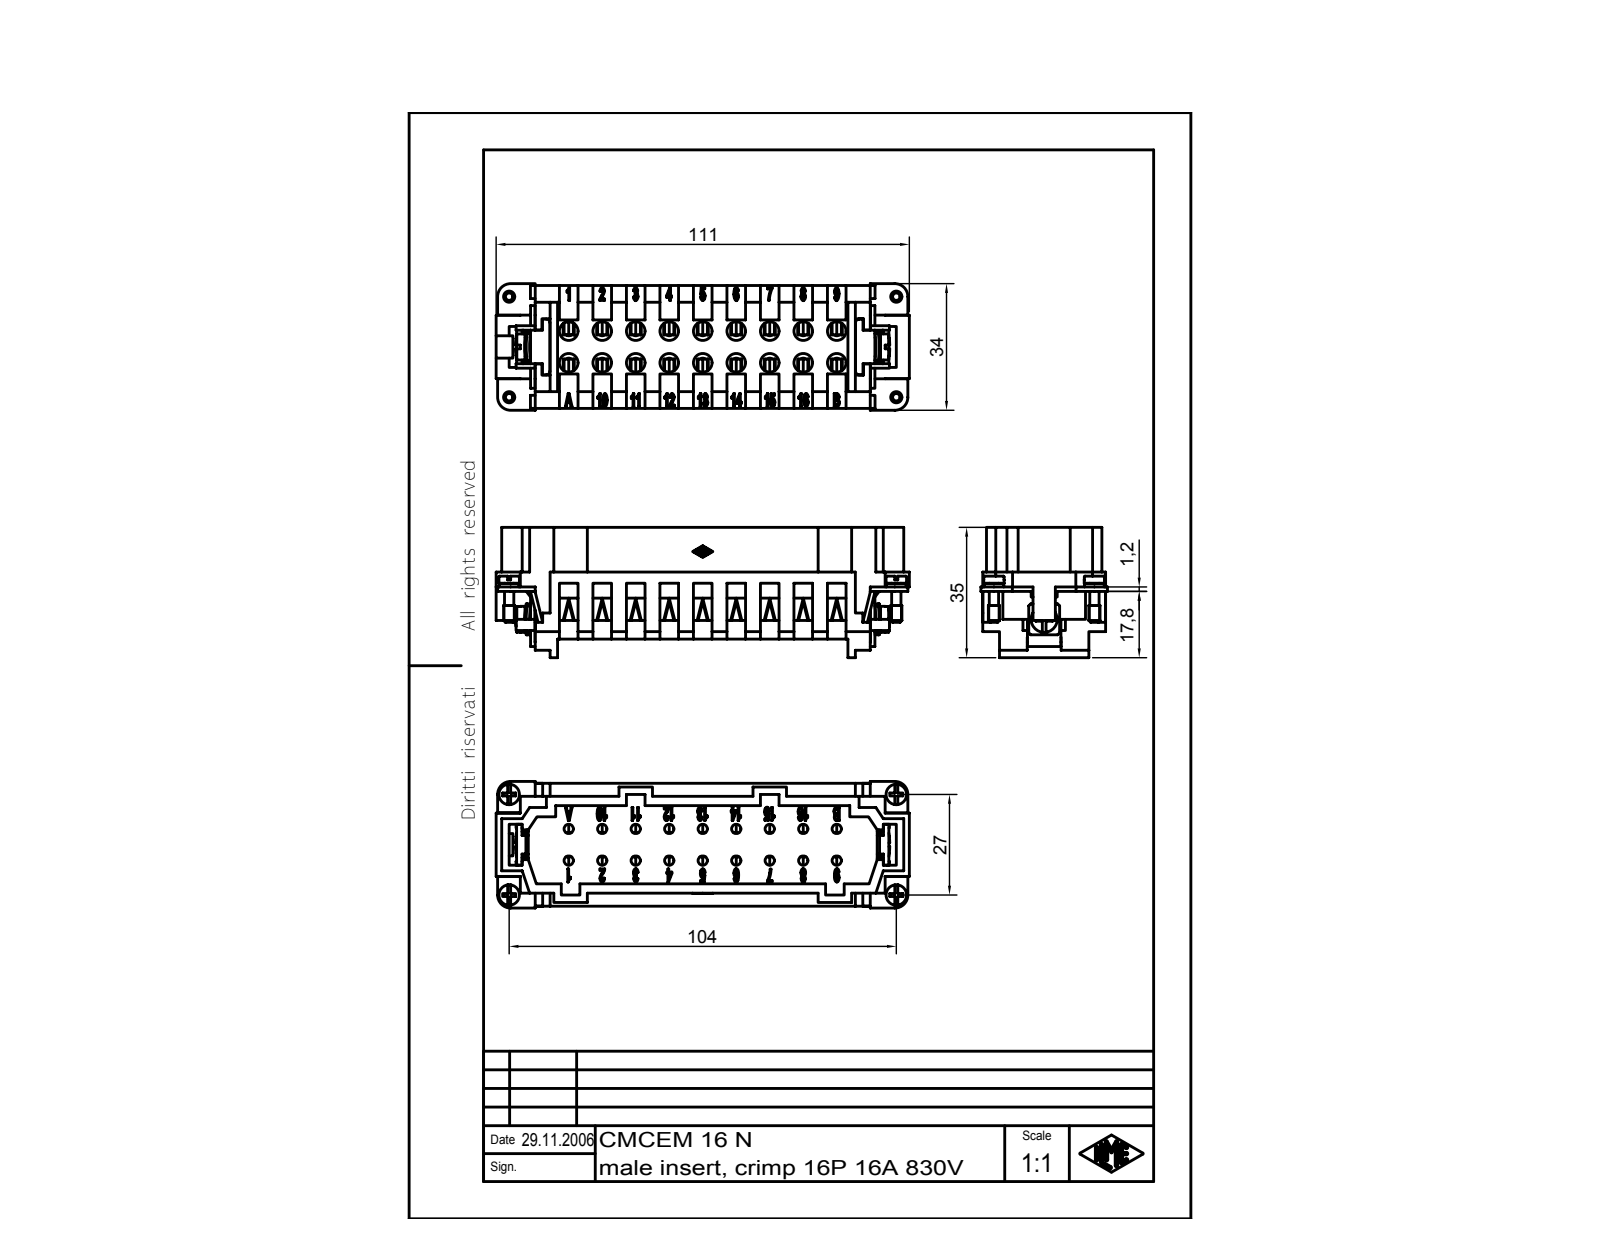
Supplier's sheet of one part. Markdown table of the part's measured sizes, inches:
| quantity | value |
| --- | --- |
| part name | CMCEM 16 N |
| STEP written by | Autodesk Inventor 7 (AUTOMOTIVE_DESIGN) |
| units | inches |
| bodies | 23 solids, 1697 faces (832 planar, 160 cylindrical, 705 other) |
| overall size | 4.37 × 1.378 × 1.339 |
| volume | 2.635 in³ |
| surface area | 53.42 in² |
| round holes (diameter × count) | 0.098 × 18, 0.197 × 18, 0.1 × 2 |
| round bosses / shafts (diameter × count) | 0.217 × 2, 0.209 × 2, 0.118 × 2, 0.098 × 2, 0.276 × 1 |
| partial cylindrical surfaces (radius × count) | 0.004 × 14, 0.039 × 2, 0.079 × 2, 0.138 × 2, 0.217 × 1 |
| main face-to-face distances | 1.063, 0.098, 0.118, 0.236, 0.709, 0.138, 0.512, 0.925, 0.197, 0.354 |
| hole center spacings | 0.354, 0.487, 0.709, 0.784, 1.063, 1.115, 1.417, 1.456 |
